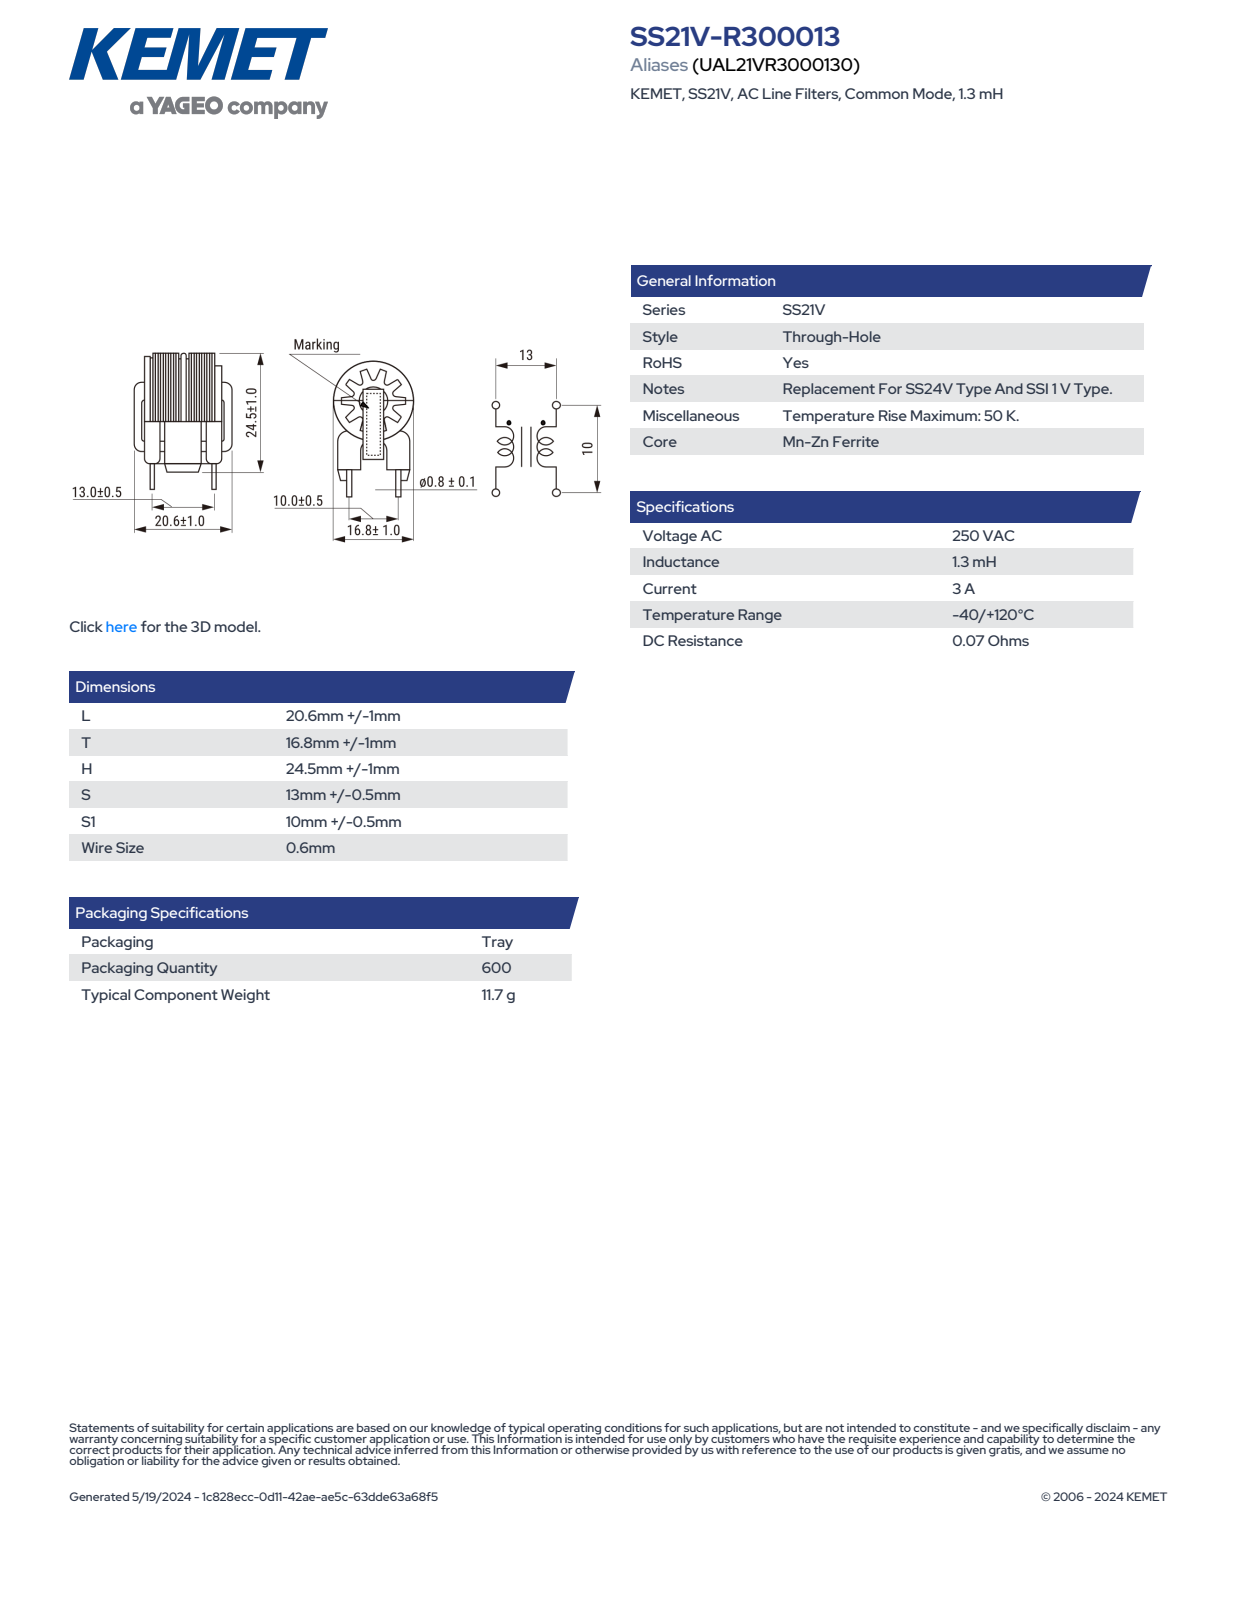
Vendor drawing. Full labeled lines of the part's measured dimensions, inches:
Part name (STEP PRODUCT): SS21V(MAX-LOGO)
STEP written by: SolidWorks 2018 (AUTOMOTIVE_DESIGN)
Units: inches
Bodies: 1 solid, 631 faces (220 planar, 212 cylindrical, 199 other)
Overall size (bounding box): 1.142 × 0.846 × 0.689
Volume: 0.266 in³ · Surface area: 8.492 in²
Round holes (diameter × count): ⌀0.224 ×1, ⌀0.236 ×1
Round bosses / shafts (diameter × count): ⌀0.031 ×4, ⌀0.563 ×1, ⌀0.559 ×1
Partial cylindrical surfaces — rounded edges, fillets, slot ends (radius × count): R0.02 ×42, R0.012 ×20, R0.067 ×20, R0.031 ×10, R0.118 ×6, R0.008 ×4, R0.039 ×4, R0.148 ×1
Main face-to-face distances: 0.297, 0.144, 0.172, 0.055, 0.117, 0.089, 0.442, 0.262, 0.191, 0.242
